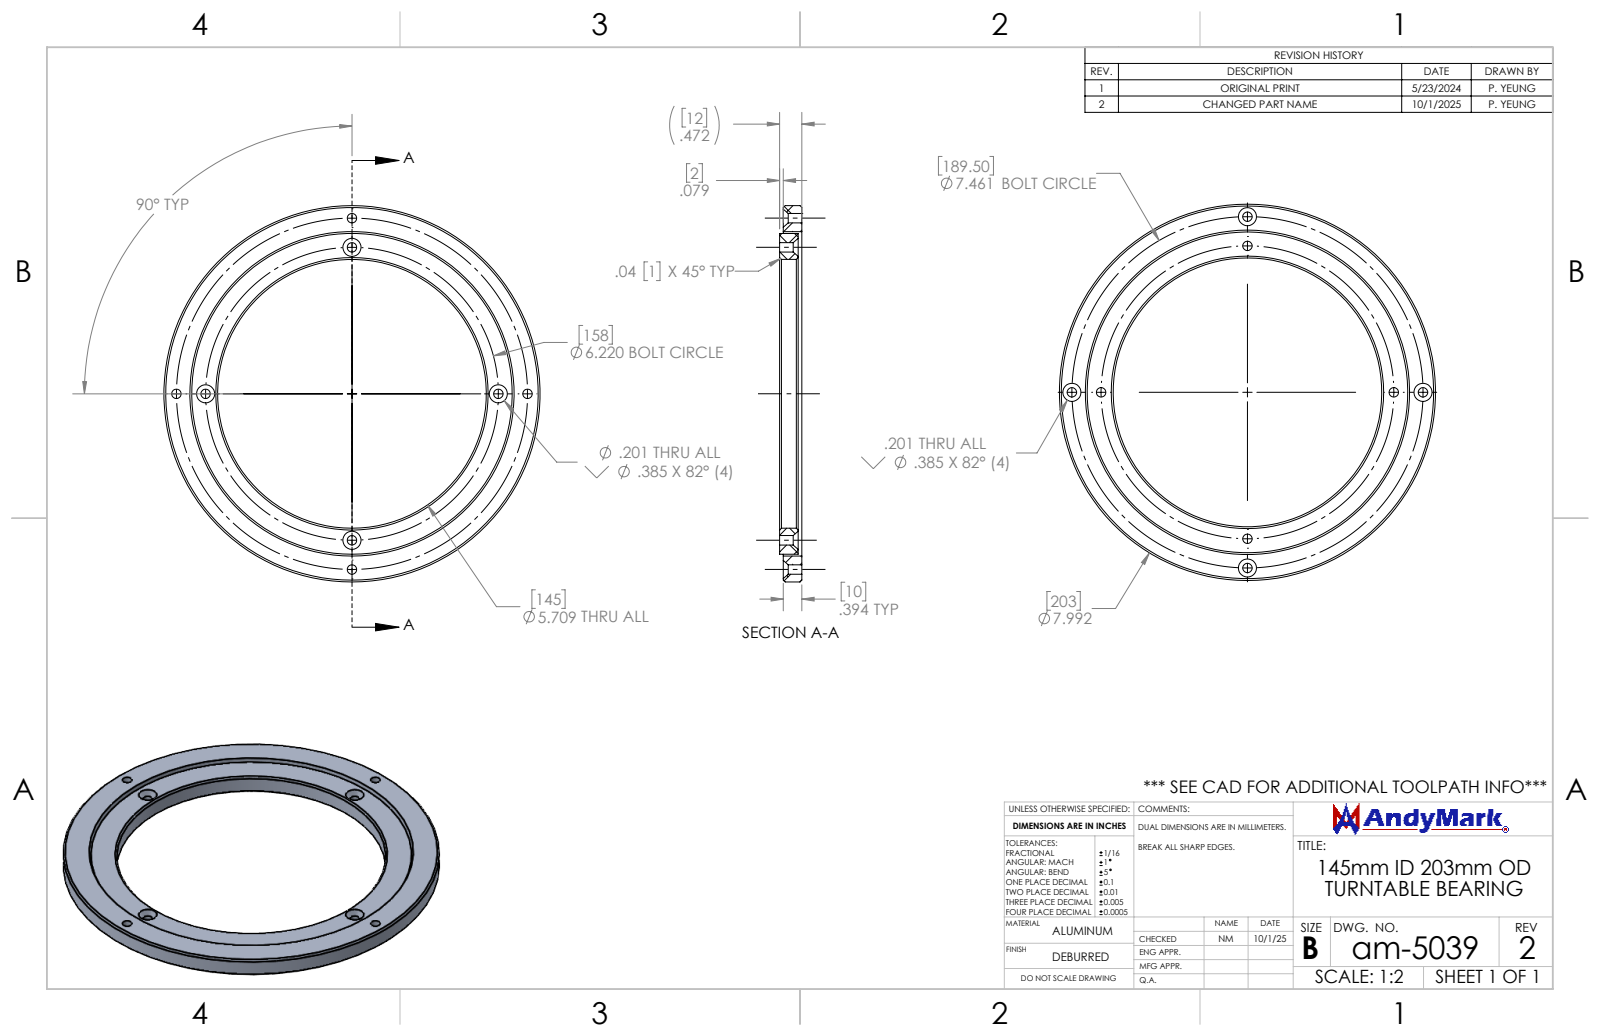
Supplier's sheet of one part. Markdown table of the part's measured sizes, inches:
| quantity | value |
| --- | --- |
| part name | 145mm ID Turntable Inner Race; 203mm OD Turntable Outer Race; am-5039 145 mm ID 203 mm OD Turntable Bearing |
| STEP written by | SolidWorks 2024 (AUTOMOTIVE_DESIGN) |
| units | inches |
| bodies | 2 solids, 52 faces (4 planar, 24 cylindrical, 24 other) |
| overall size | 7.992 × 7.992 × 0.472 |
| volume | 9.141 in³ |
| surface area | 80.66 in² |
| round holes (diameter × count) | 0.201 × 8, 5.709 × 1, 6.89 × 1 |
| round bosses / shafts (diameter × count) | 7.992 × 1, 6.811 × 1 |
| main face-to-face distances | 0.394, 0.079, 0.472, 0.315 |
| hole center spacings | 4.857, 0.62, 3.11, 3.73, 4.398, 5.276, 6.841, 6.22 |
